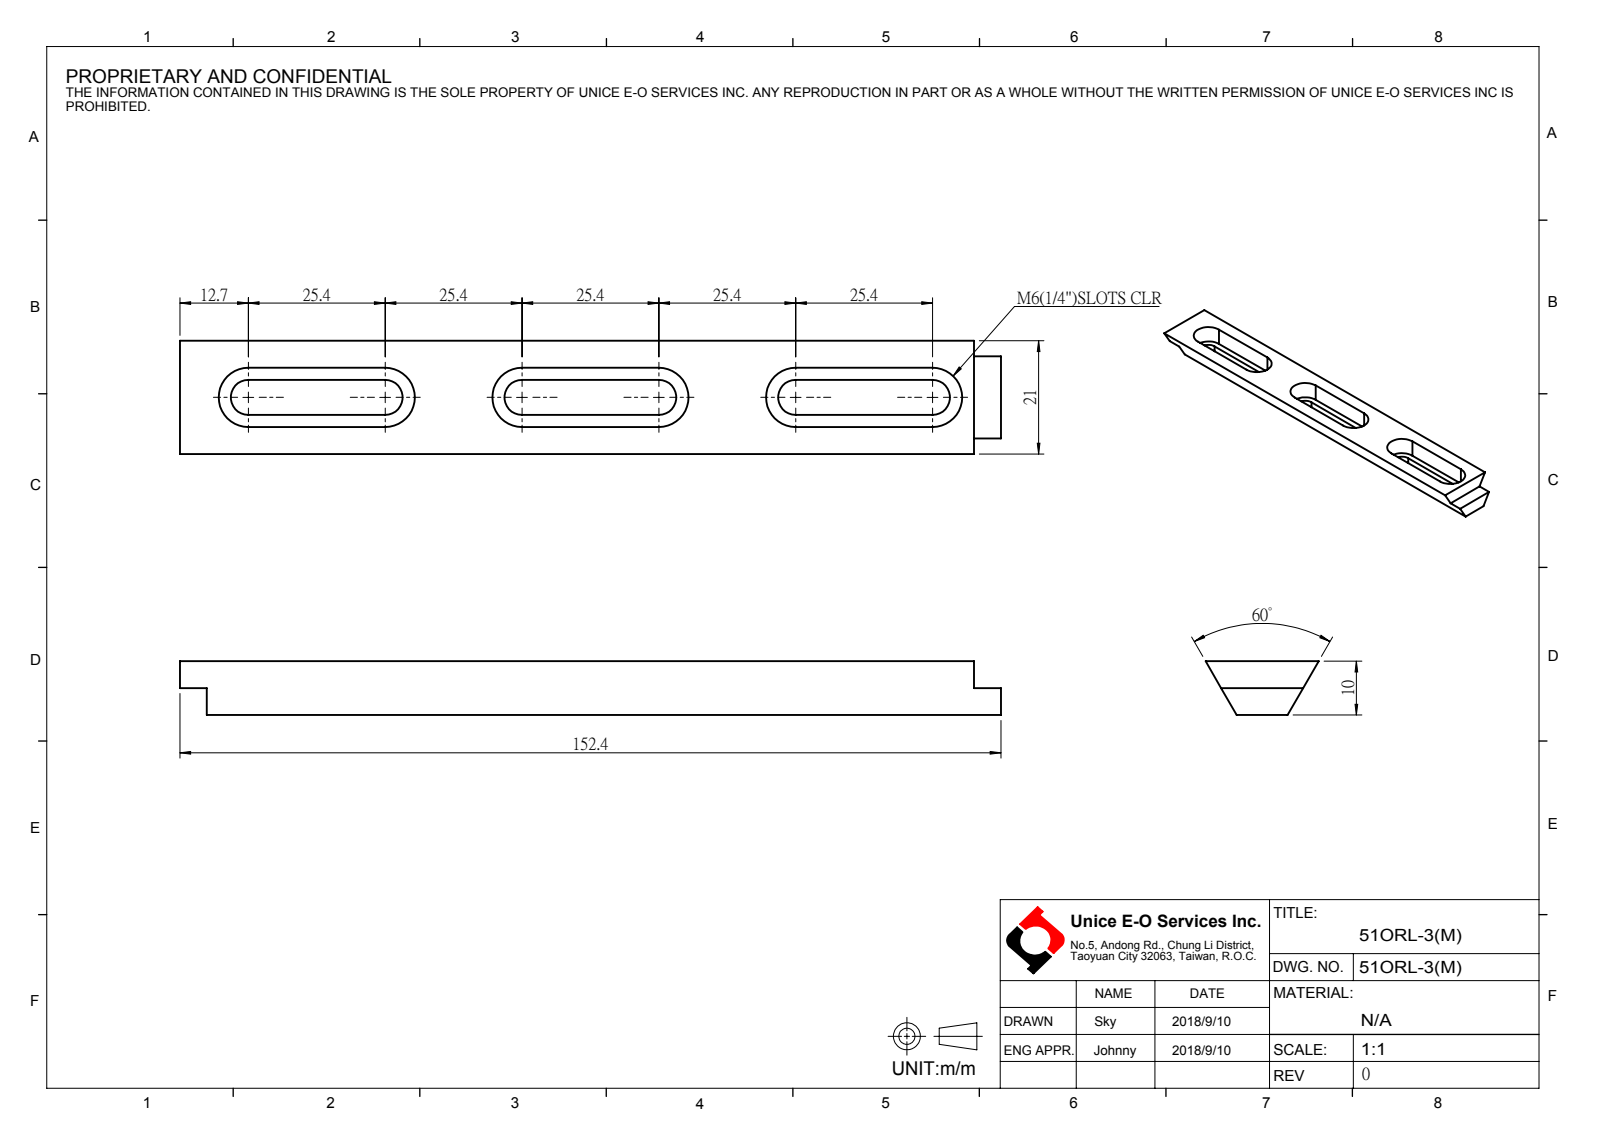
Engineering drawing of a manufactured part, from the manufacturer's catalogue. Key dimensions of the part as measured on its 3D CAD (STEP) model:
Part name (STEP PRODUCT): 51ORL-3(M)
STEP written by: SolidWorks 2016 (AUTOMOTIVE_DESIGN)
Units: millimetres
Bodies: 0 solids, 37 faces (25 planar, 12 cylindrical, 0 other)
Overall size (bounding box): 152.4 × 21 × 10
Partial cylindrical surfaces — rounded edges, fillets, slot ends (radius × count): R3.25 ×6, R5.5 ×6
Main face-to-face distances: 10, 6.5, 2.25, 8.75, 3.5, 11, 5, 147.4, 1.5, 152.4
